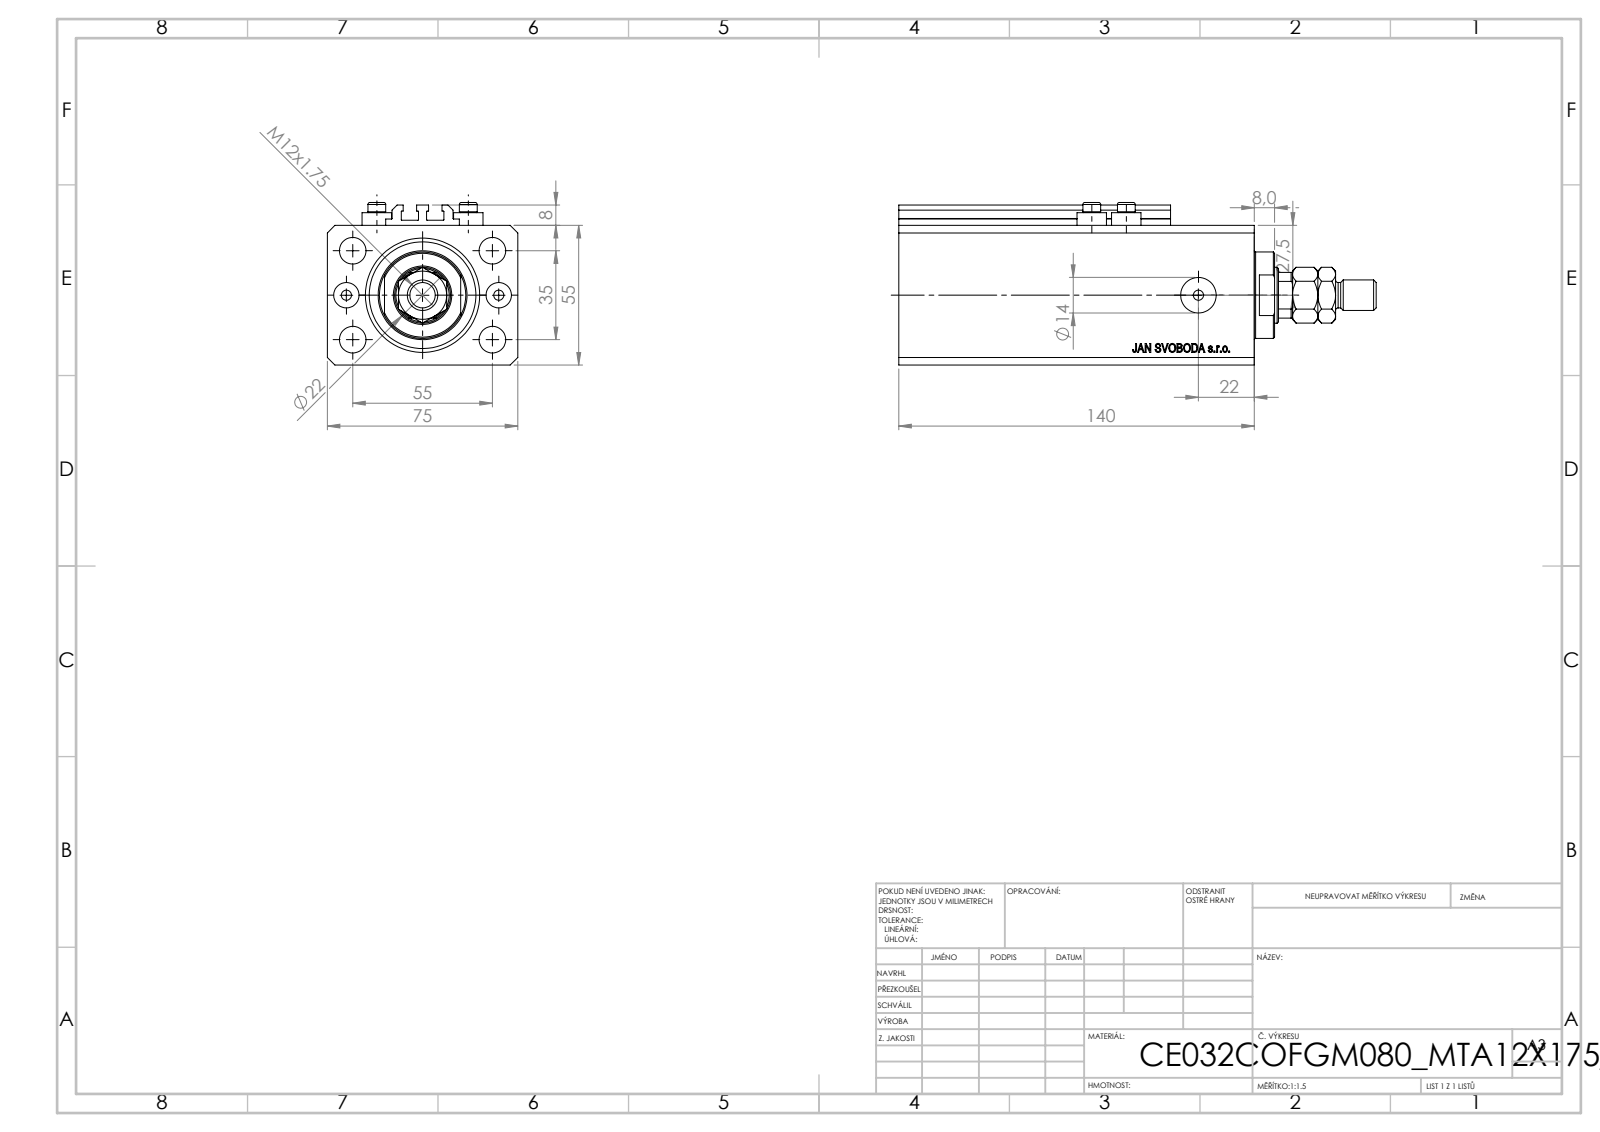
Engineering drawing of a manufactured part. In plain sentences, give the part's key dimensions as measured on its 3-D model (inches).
The part is named "V250CE_C_Body; ALLEN BOLT V250CE; V250CE_C_VCP; MTA (+1 more)". Its 3-D file was written by "SolidWorks 2019 (CONFIG_CONTROL_DESIGN)". It is 9 solids with 1082 faces: 518 planar, 90 cylindrical and 474 other. Overall it measures 7.398 by 2.953 by 2.52 inches. Its volume is 31.72 cubic inches and its surface area 179.4 square inches. Round holes: 8 of diameter 0.157, 5 of diameter 0.413, 2 of diameter 0.394, 2 of diameter 0.551, 1 of diameter 0.866, 1 of diameter 1.26, 1 of diameter 1.772. Round bosses or shafts: 4 of diameter 0.457, 4 of diameter 0.276, 1 of diameter 1.339, 1 of diameter 0.472, 1 of diameter 0.394. Partial cylindrical surfaces (rounded edges, fillets, slot ends): 10 of radius 0.008, 1 of radius 0.413. The main face-to-face distances are 2.165, 2.953, 5.512, 4.445, 1.067, 0.098, 0.39, 4.055, 5.122, 0.079. The hole center spacings are 0.696, 1.283, 2.366, 0.535, 1.181, 1.378, 1.417, 1.515.
